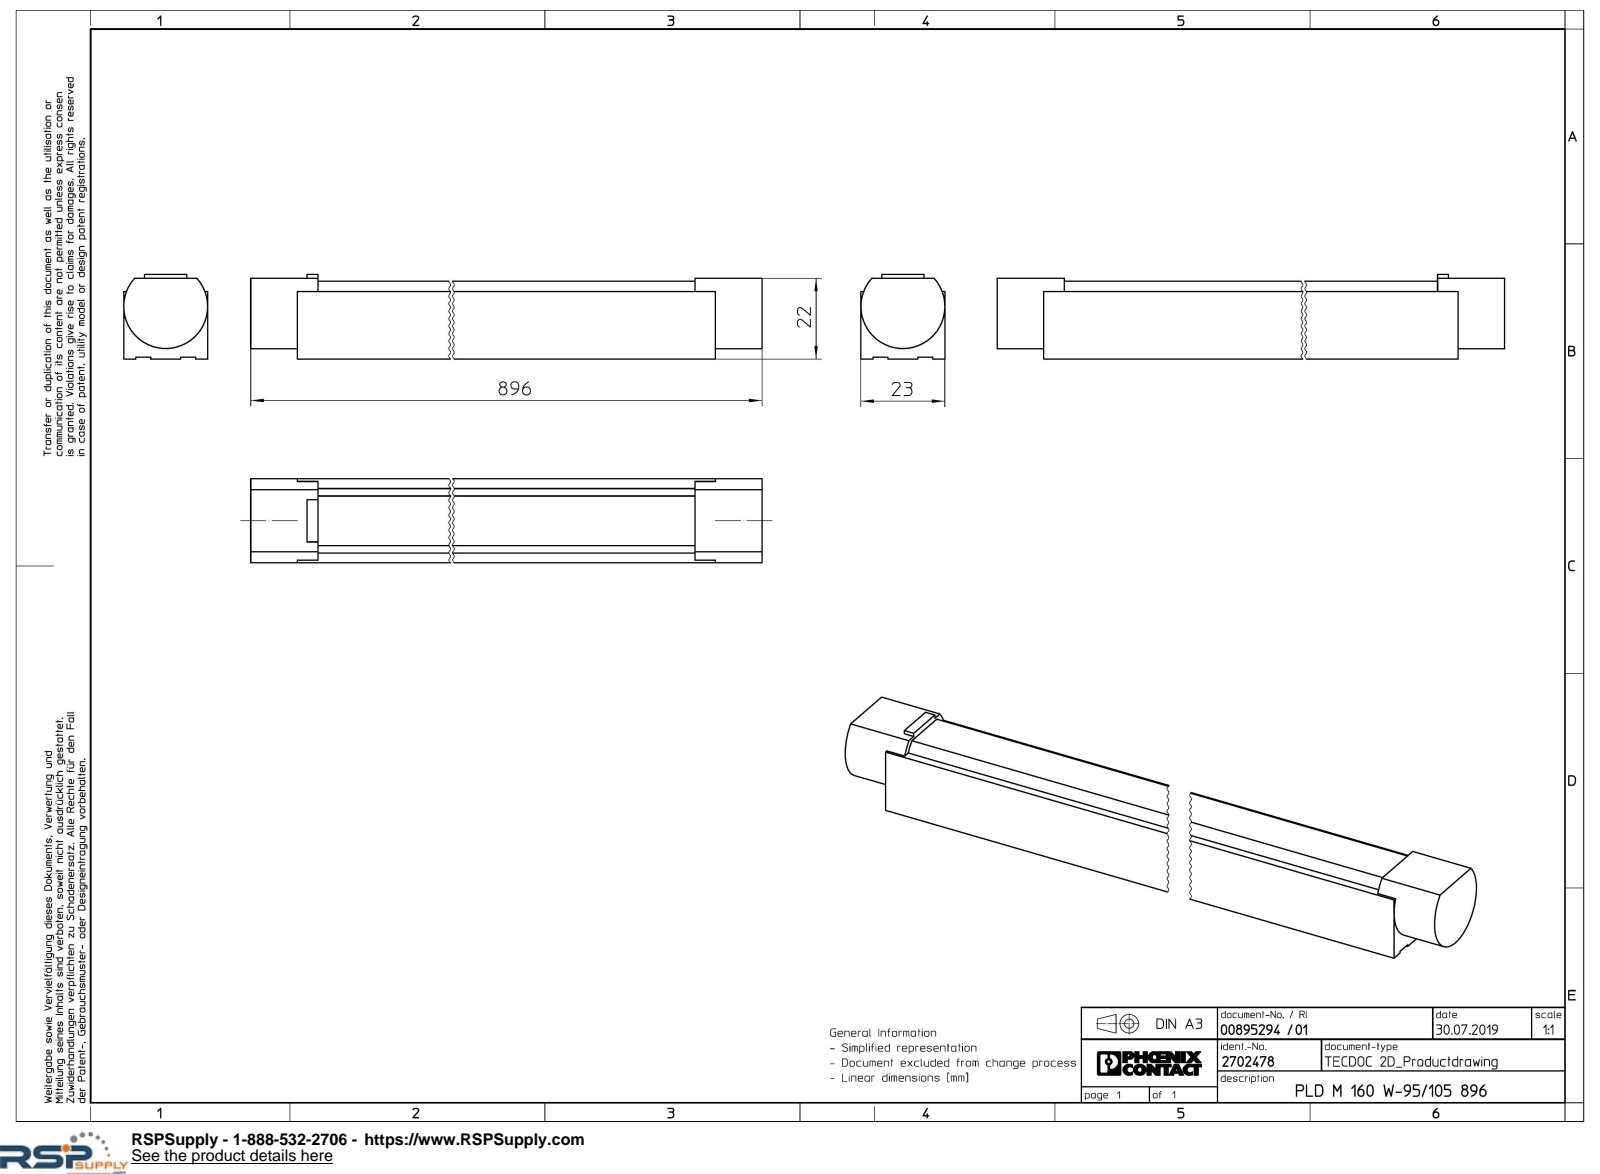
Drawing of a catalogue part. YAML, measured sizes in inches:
part_name: "PLD_M_160_W_95_105_896-select"
step_written_by: "Creo Elements/Direct Modeling 20.1A 29-Sep-2018 (C) Parametric Technology GmbH (AUTOMOTIVE_DESIGN)"
units: inches
bodies: {solids: 1, faces: 40, planar: 32, cylindrical: 8, other: 0}
overall_size: [35.276, 0.89, 0.886]
volume: 24.18
surface_area: 120.4
round_holes:
  - {diameter: 0.173, count: 2}
partial_cylinders:
  - {radius: 0.374, count: 1}
  - {radius: 0.443, count: 1}
face_to_face_distances: [0.886, 0.819, 0.02, 0.799, 0.709, 0.689, 0.11, 0.128, 0.285, 0.6]
hole_center_spacings: [33.465]
